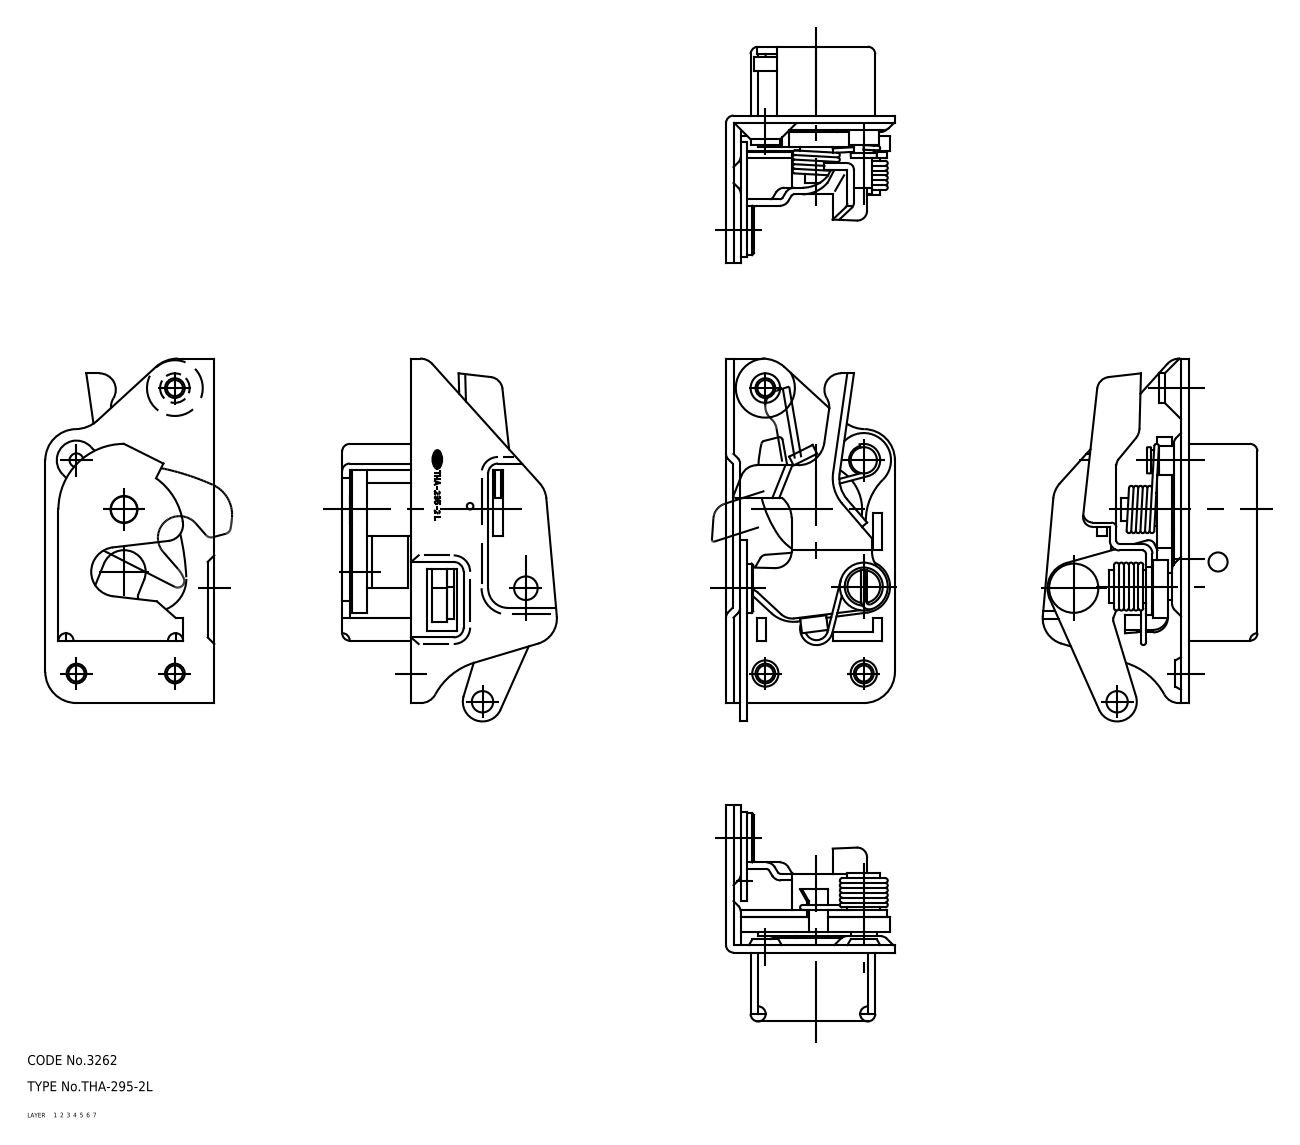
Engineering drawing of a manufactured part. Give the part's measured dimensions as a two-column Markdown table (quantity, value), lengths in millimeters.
| quantity | value |
| --- | --- |
| part name | spring_B_mr; spring_A_mr; pin_C_mr; pin_B_mr (+8 more) |
| STEP written by | CADfix (AUTOMOTIVE_DESIGN) |
| units | millimeters |
| bodies | 12 solids, 564 faces (0 planar, 0 cylindrical, 564 other) |
| overall size | 110.61 × 65.45 × 51.5 |
| volume | 52 311 mm³ |
| surface area | 45 580 mm² |
